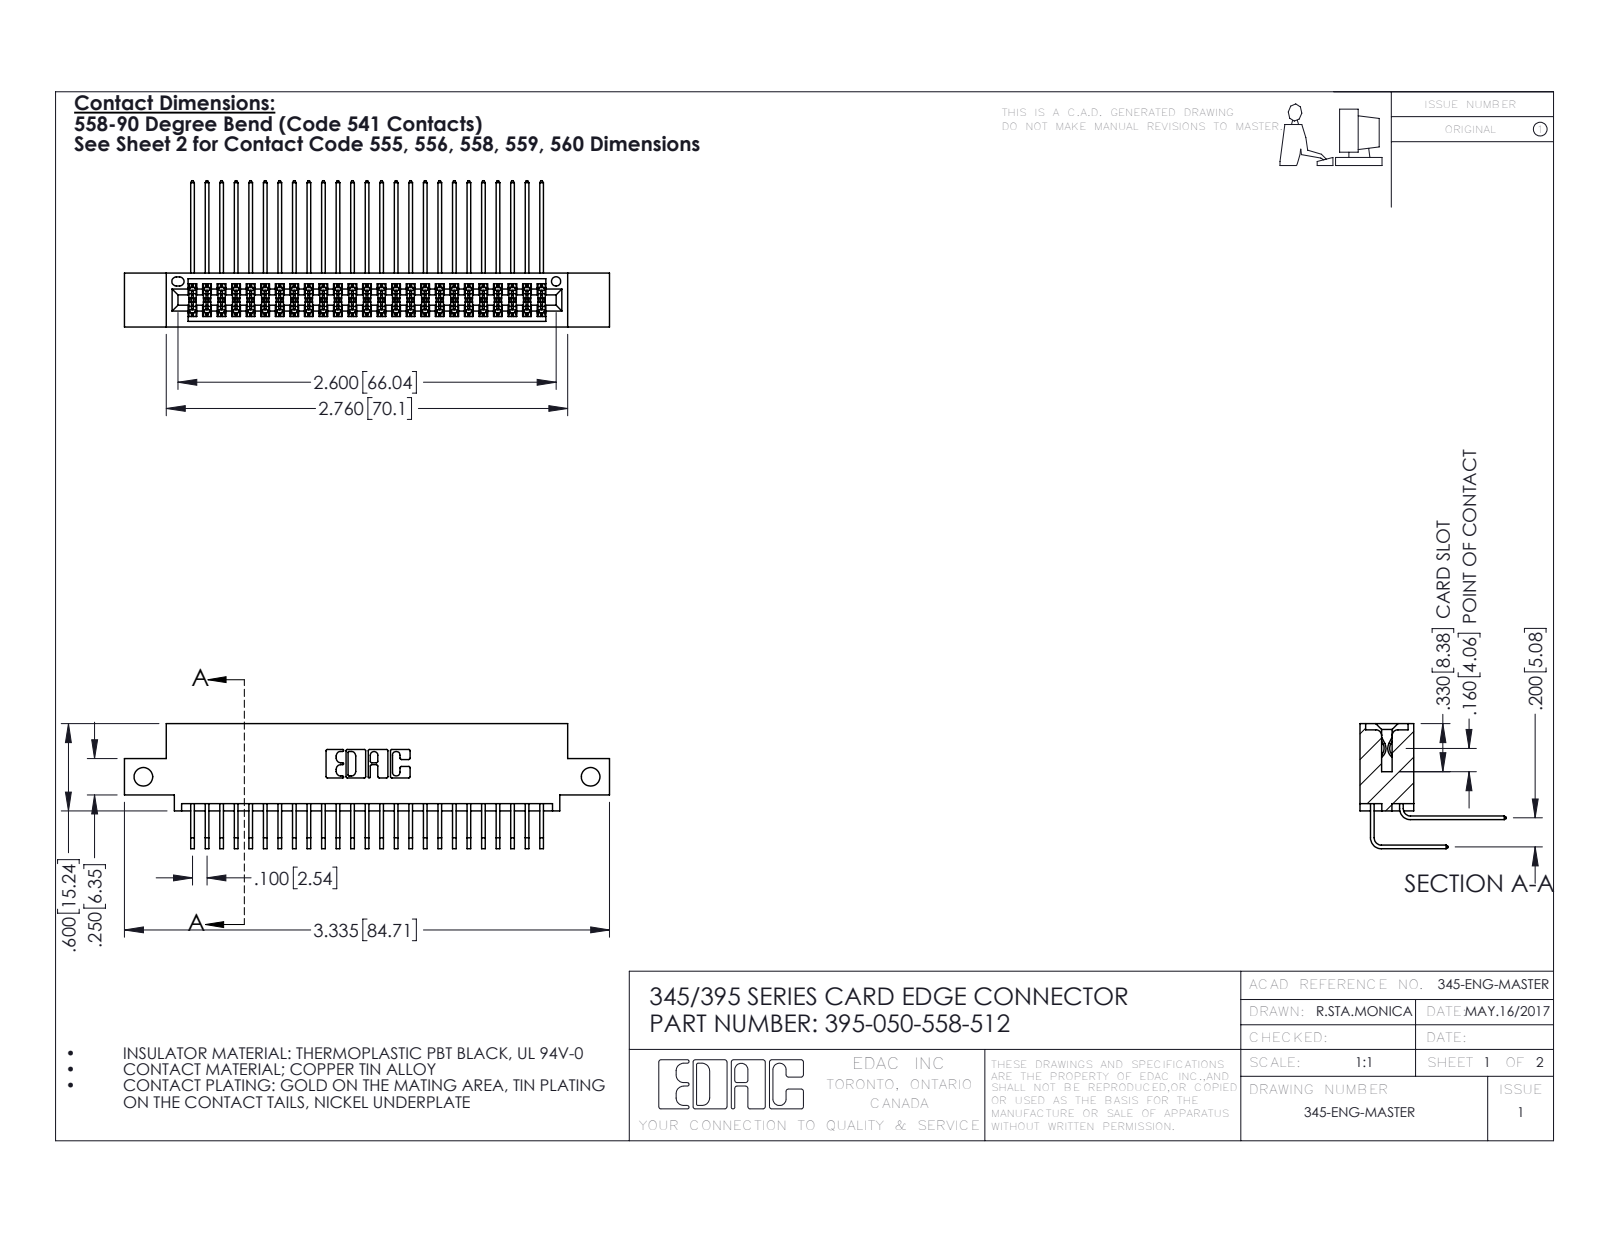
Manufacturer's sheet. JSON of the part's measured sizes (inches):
{"part_name": "345-292-001_558 559 Tail - 1; 345-292-001_558 Tail - 2; 345 Part_0.110 Offset - Side Mount; 395-050-558-512", "step_written_by": "SolidWorks 2016 (CONFIG_CONTROL_DESIGN)", "units": "inches", "bodies": {"solids": 51, "faces": 2730, "planar": 1834, "cylindrical": 896, "other": 0}, "overall_size": [3.335, 1.005, 0.859], "volume_in3": 0.5, "surface_area_in2": 20.31, "round_holes": [[0.128, 2], [0.064, 1]], "partial_cylinders_radius": [[0.006, 76], [0.01, 22], [0.007, 6], [0.031, 6], [0.026, 3], [0.014, 2], [0.019, 2], [0.022, 2]], "face_to_face_distances": [0.072, 0.298, 0.2, 0.37, 0.098, 0.272, 0.025, 0.225, 0.025, 0.175], "hole_center_spacings": [3.075]}
